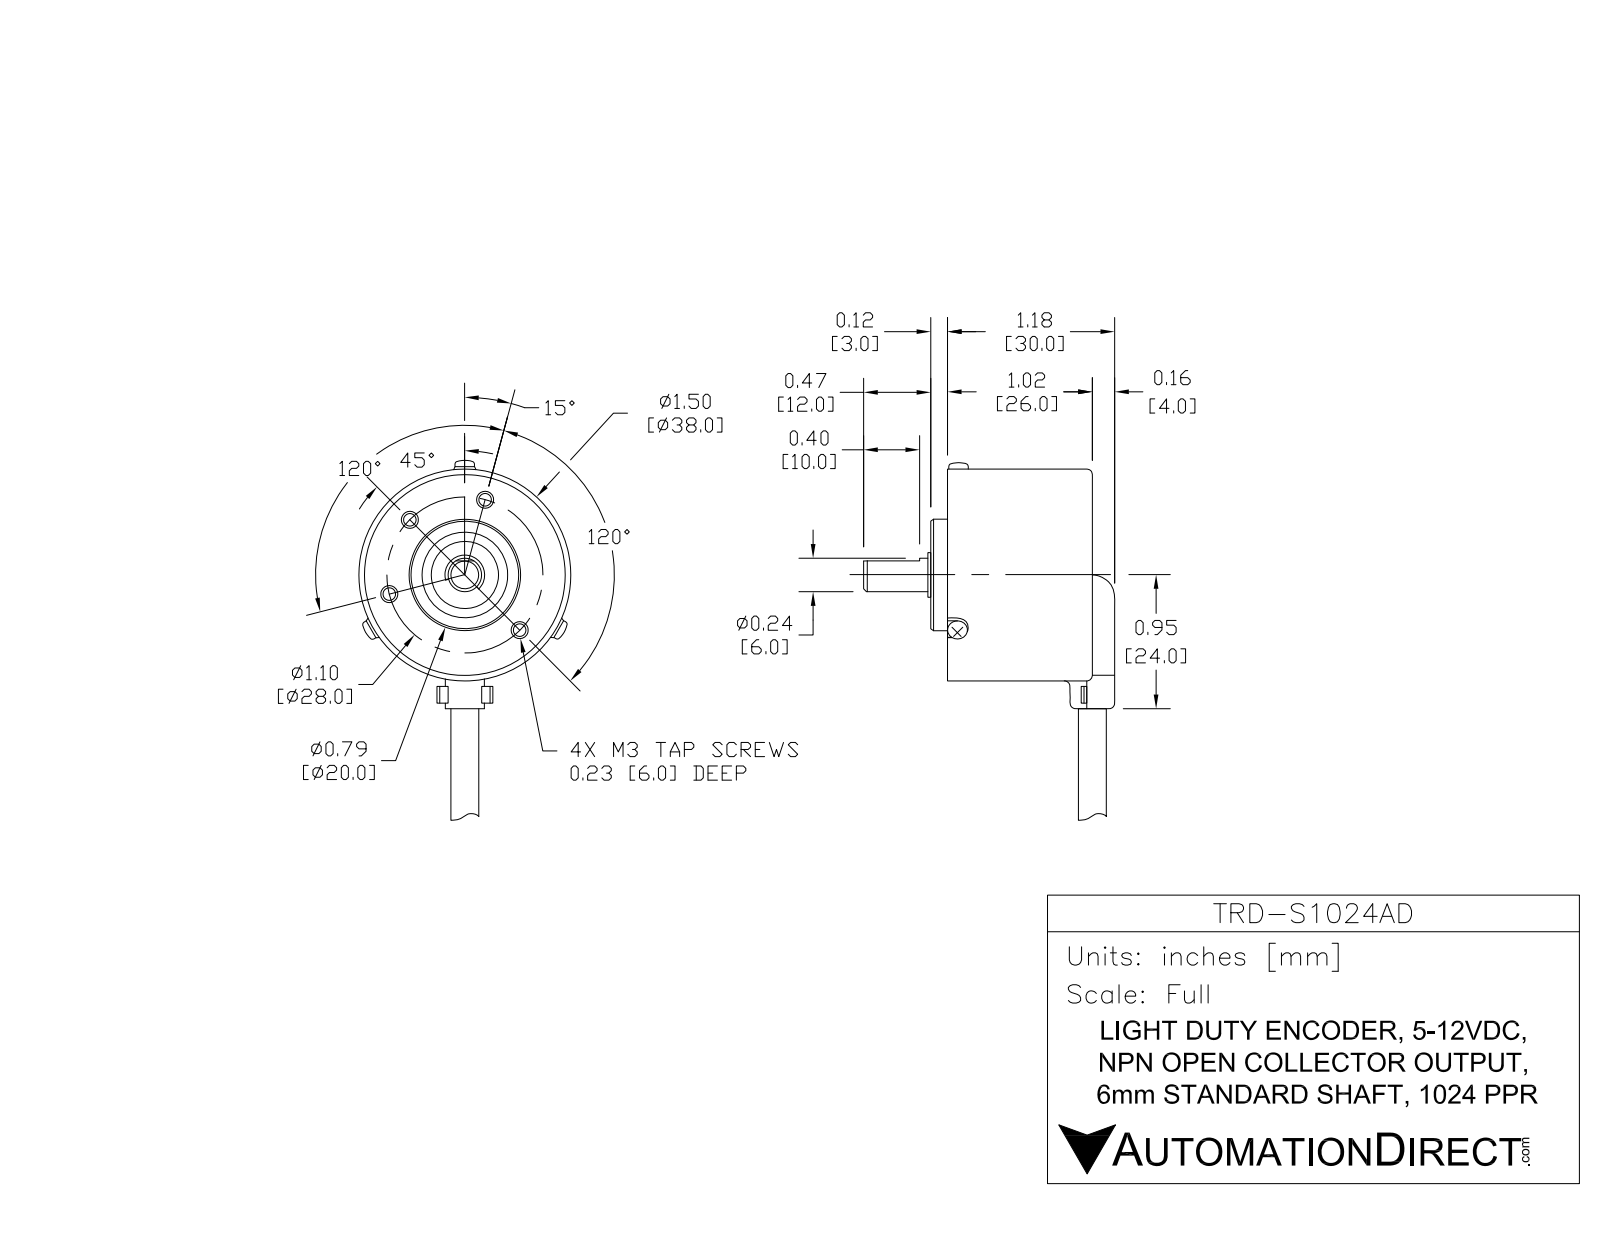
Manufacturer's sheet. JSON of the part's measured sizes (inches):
{"part_name": "TRD-S1024AD", "step_written_by": "SolidWorks 2016 (AUTOMOTIVE_DESIGN)", "units": "inches", "bodies": {"solids": 3, "faces": 257, "planar": 98, "cylindrical": 100, "other": 59}, "overall_size": [7.189, 1.768, 1.496], "volume_in3": 2.068, "surface_area_in2": 13.85, "round_holes": [[0.118, 4], [0.205, 1], [0.256, 1], [1.409, 1]], "round_bosses_or_shafts": [[1.496, 1], [0.787, 1], [0.591, 1], [0.315, 1], [0.236, 1], [0.197, 1], [0.193, 1]], "partial_cylinders_radius": [[0.016, 11], [0.004, 4], [0.13, 3], [0.748, 3], [0.008, 2], [0.02, 2], [0.146, 2], [0.11, 1]], "face_to_face_distances": [1.024, 0.118, 1.142, 0.02, 0.138, 0.803, 1.161, 0.354, 0.335, 0.217], "hole_center_spacings": [0.551, 0.955, 0.954, 1.102]}
